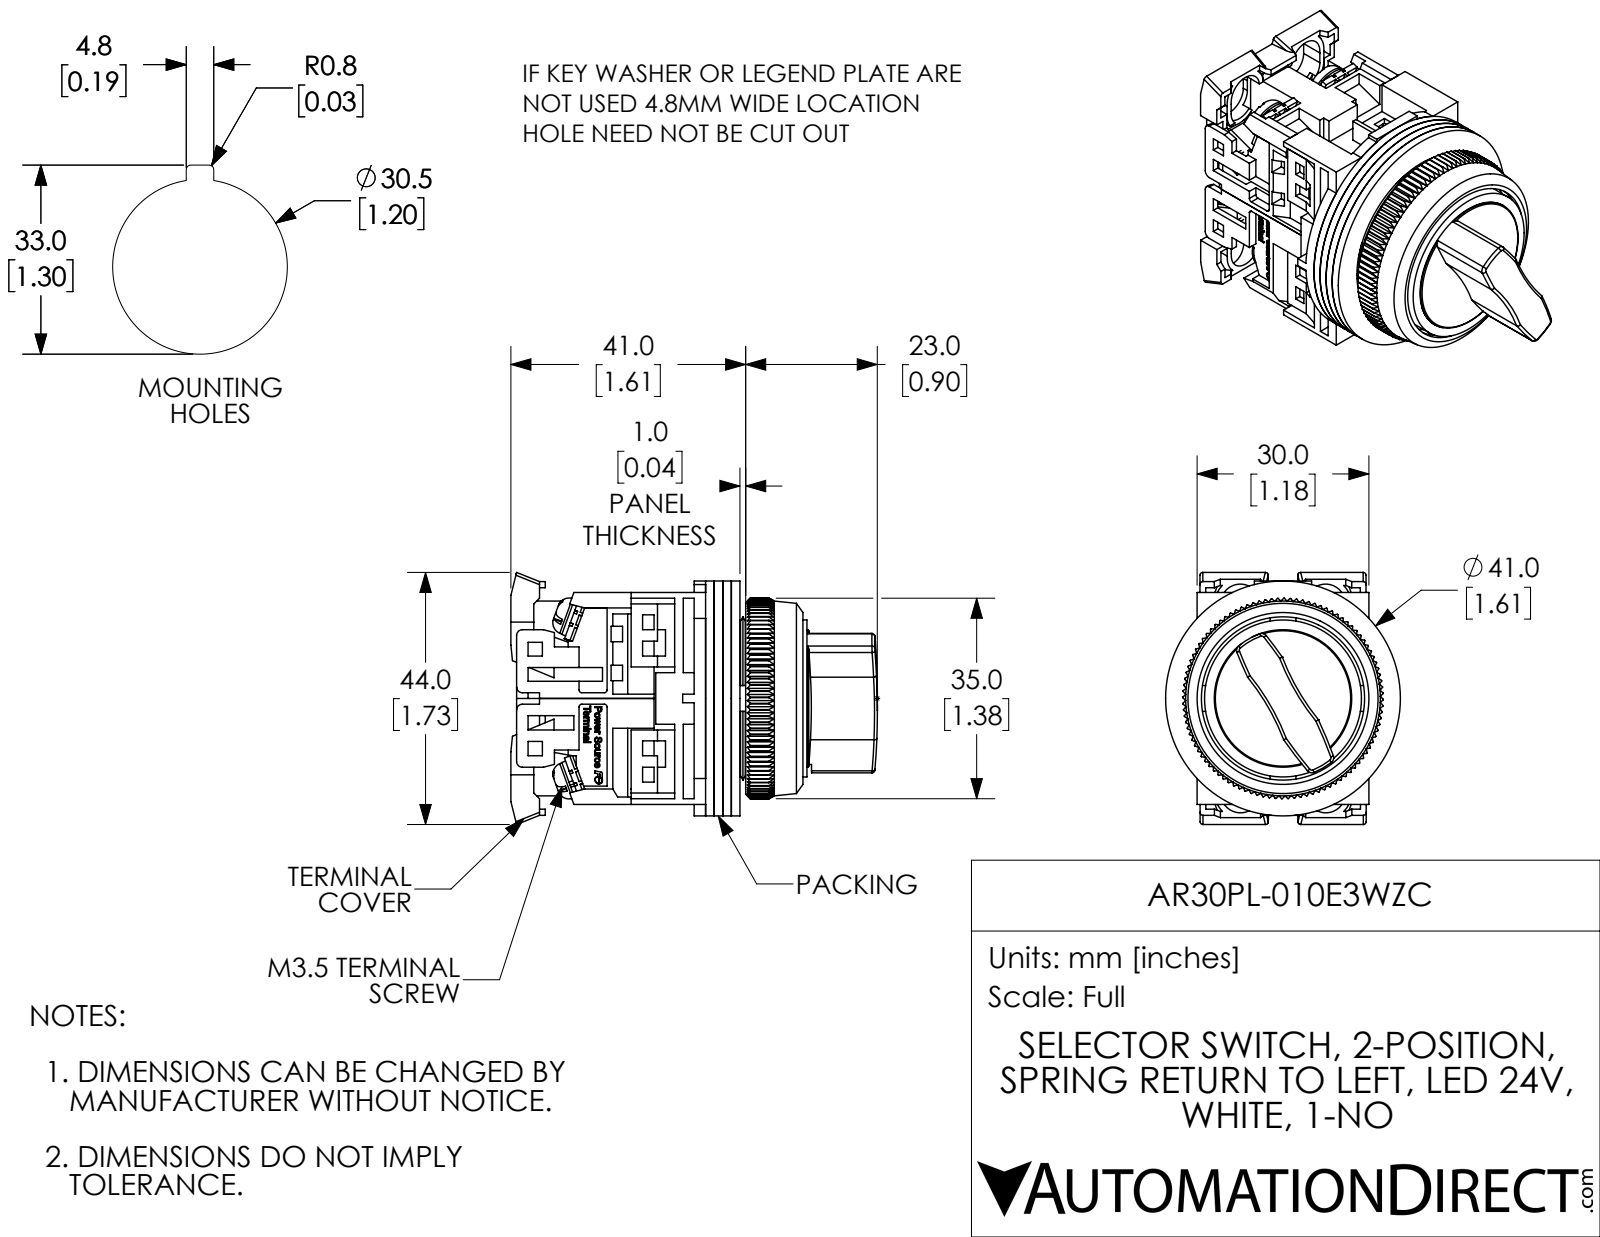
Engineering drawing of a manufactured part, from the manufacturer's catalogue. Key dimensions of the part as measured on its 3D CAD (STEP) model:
Part name (STEP PRODUCT): AR30PL-010E3WZC
STEP written by: SolidWorks 2017 (AUTOMOTIVE_DESIGN)
Units: inches
Bodies: 25 solids, 2434 faces (1731 planar, 305 cylindrical, 398 other)
Overall size (bounding box): 2.52 × 1.732 × 1.614
Volume: 2.238 in³ · Surface area: 59.31 in²
Round holes (diameter × count): ⌀0.138 ×8, ⌀0.142 ×4, ⌀0.118 ×1, ⌀0.472 ×1, ⌀0.709 ×1, ⌀0.768 ×1, ⌀0.827 ×1, ⌀1.122 ×1, ⌀1.181 ×1, ⌀1.252 ×1
Round bosses / shafts (diameter × count): ⌀0.26 ×4, ⌀0.138 ×4, ⌀0.063 ×2, ⌀1.614 ×1, ⌀1.15 ×1, ⌀1.079 ×1, ⌀0.945 ×1, ⌀0.886 ×1
Partial cylindrical surfaces — rounded edges, fillets, slot ends (radius × count): R0.059 ×16, R0.02 ×12, R0.039 ×8, R0.138 ×4, R0.177 ×4, R0.118 ×2, R1.575 ×2, R2.953 ×2
Main face-to-face distances: 0.059, 0.118, 0.177, 0.039, 0.079, 1.417, 1.358, 0.811, 0.197, 0.02
Hole centre spacings: 0.579, 0.61
